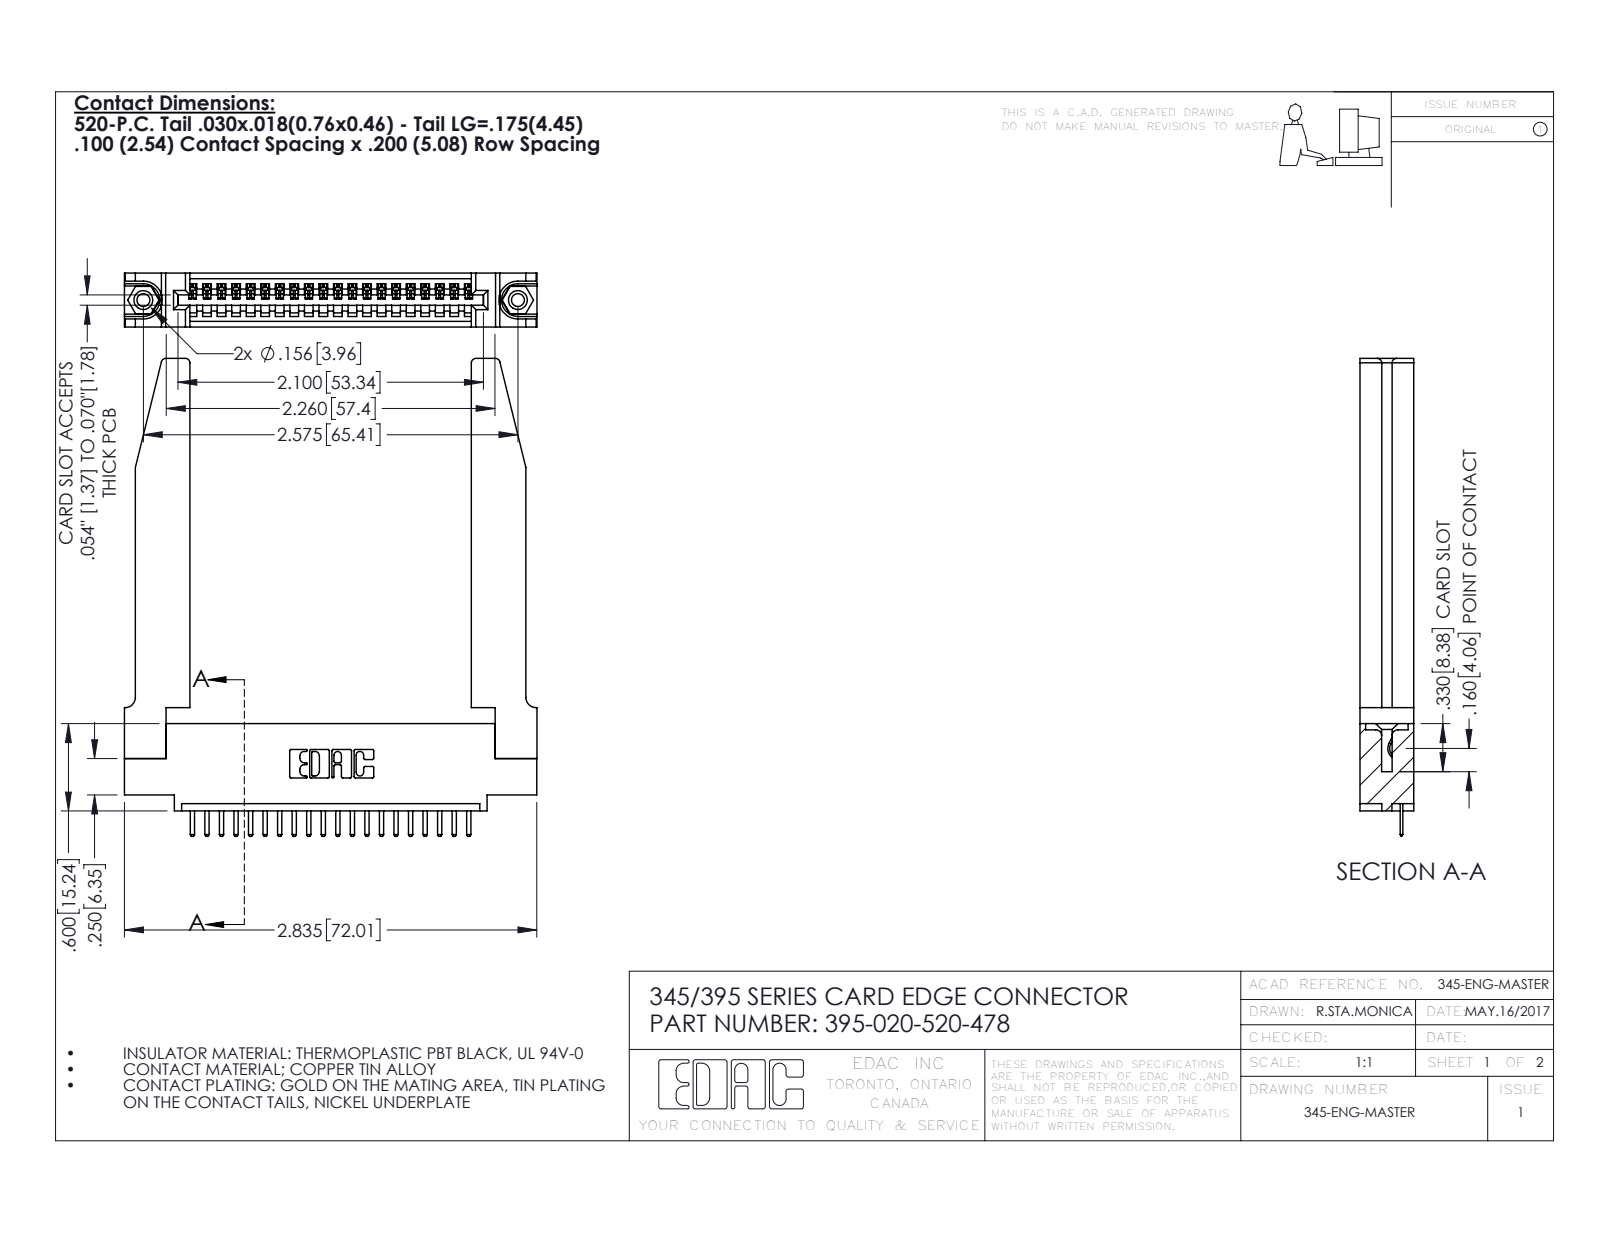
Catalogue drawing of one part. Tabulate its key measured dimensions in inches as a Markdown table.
| quantity | value |
| --- | --- |
| part name | 395-020-520-478; 345-250-001_345-250-001-102; 345-292-001_345-293-120; 345 Part_0.110 Offset - 0.156 Dia-TH (+1 more) |
| STEP written by | SolidWorks 2016 (CONFIG_CONTROL_DESIGN) |
| units | inches |
| bodies | 25 solids, 1604 faces (1066 planar, 486 cylindrical, 52 other) |
| overall size | 3.285 × 2.836 × 0.37 |
| volume | 0.873 in³ |
| surface area | 23.43 in² |
| round holes (diameter × count) | 0.089 × 2, 0.125 × 2, 0.156 × 2, 0.064 × 1 |
| round bosses / shafts (diameter × count) | 0.155 × 2 |
| partial cylindrical surfaces (radius × count) | 0.01 × 42, 0.006 × 40, 0.01 × 22, 0.03 × 8, 0.007 × 6, 0.031 × 6, 0.026 × 3, 0.031 × 2 |
| main face-to-face distances | 0.37, 0.072, 0.298, 0.148, 0.15, 0.2, 0.098, 0.272, 0.025, 0.22 |
| hole center spacings | 0.27, 2.341, 2.575 |
